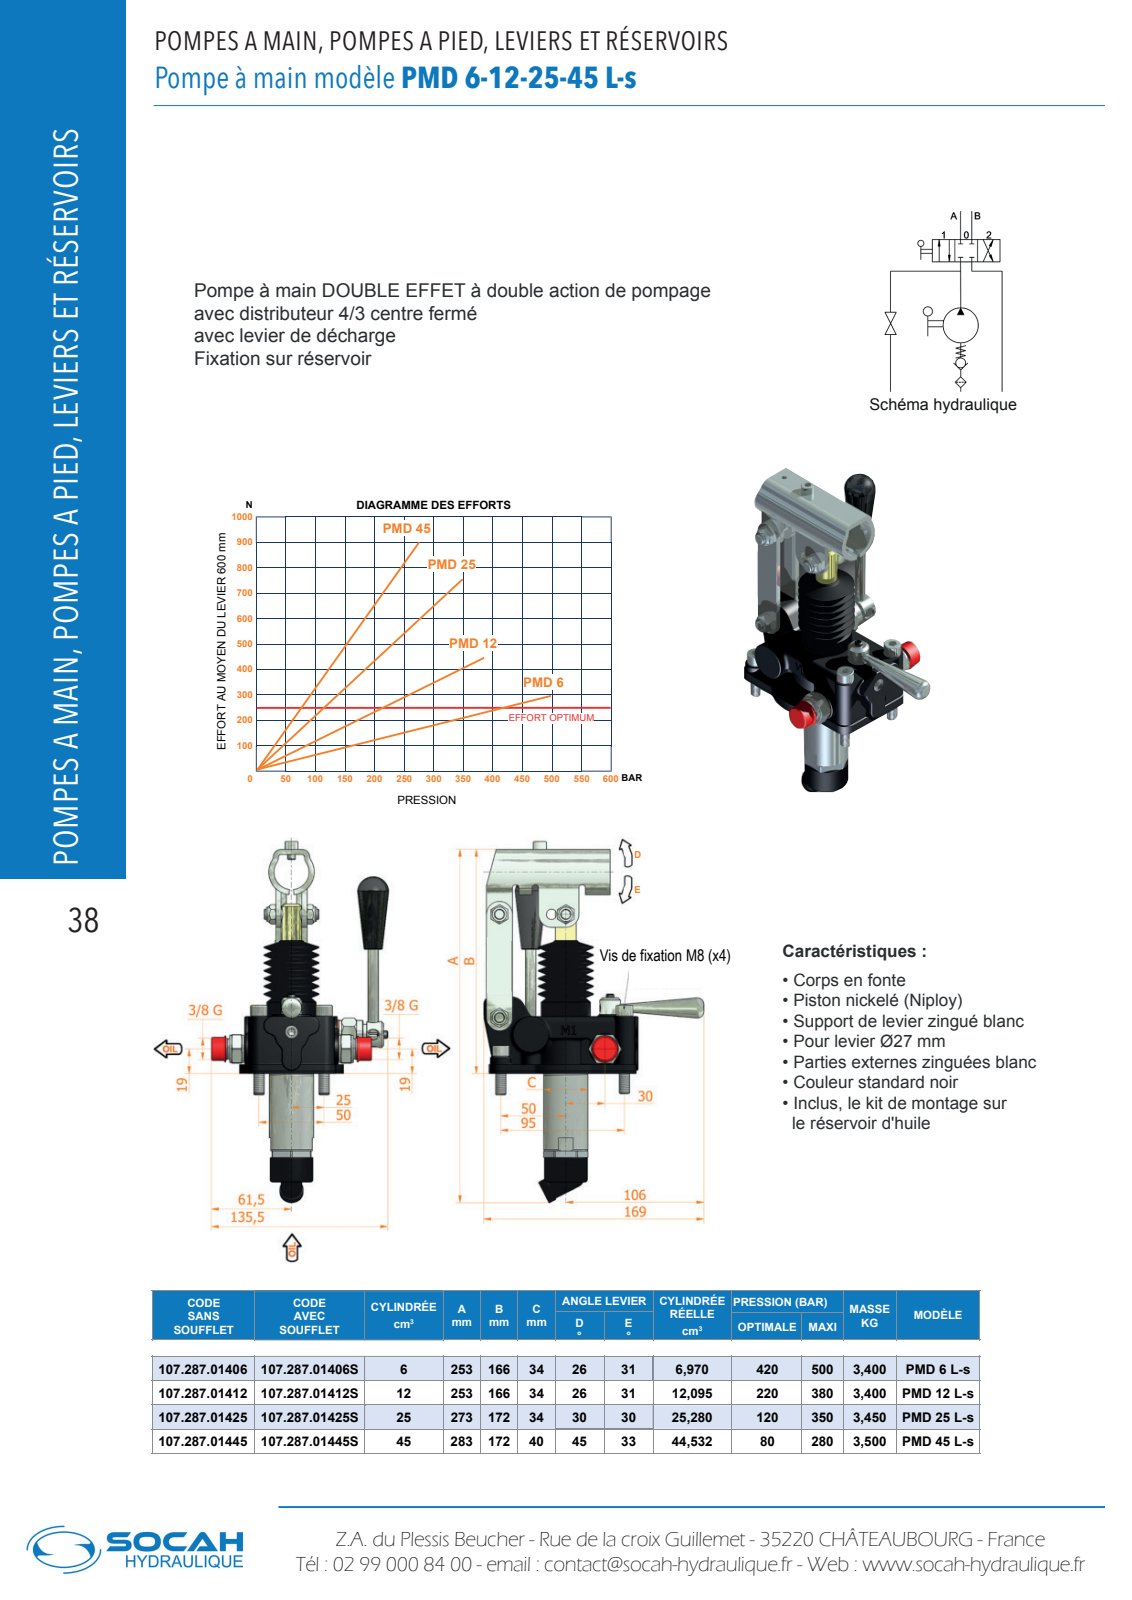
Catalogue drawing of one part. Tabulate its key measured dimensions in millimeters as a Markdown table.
| quantity | value |
| --- | --- |
| part name | 6056.0047.10.50 Derivazione 2 |
| STEP written by | Autodesk Inventor 2013 (AUTOMOTIVE_DESIGN) |
| units | millimeters |
| bodies | 15 solids, 1568 faces (719 planar, 357 cylindrical, 492 other) |
| overall size | 277.85 × 169 × 136.22 |
| volume | 9 916 mm³ |
| surface area | 158 821 mm² |
| round holes (diameter × count) | 8 × 7, 14 × 4, 4.92 × 3, 5 × 3, 4 × 1, 7.5 × 1, 9 × 1, 10 × 1, 13.5 × 1, 16 × 1, 20 × 1, 21 × 1 |
| round bosses / shafts (diameter × count) | 13 × 4, 12 × 4, 8.5 × 4, 8 × 4, 6 × 4, 20 × 3, 18 × 3, 16 × 3 |
| partial cylindrical surfaces (radius × count) | 1 × 30, 0.2 × 24, 0.1 × 16, 5 × 16, 2 × 14, 3 × 9, 8 × 9, 0.36 × 6 |
| main face-to-face distances | 4, 20, 5, 2, 37, 16, 42, 44, 24, 1 |
| hole center spacings | 25.5, 27.31, 50, 51.48, 55.9, 87.64, 93.41, 95 |
